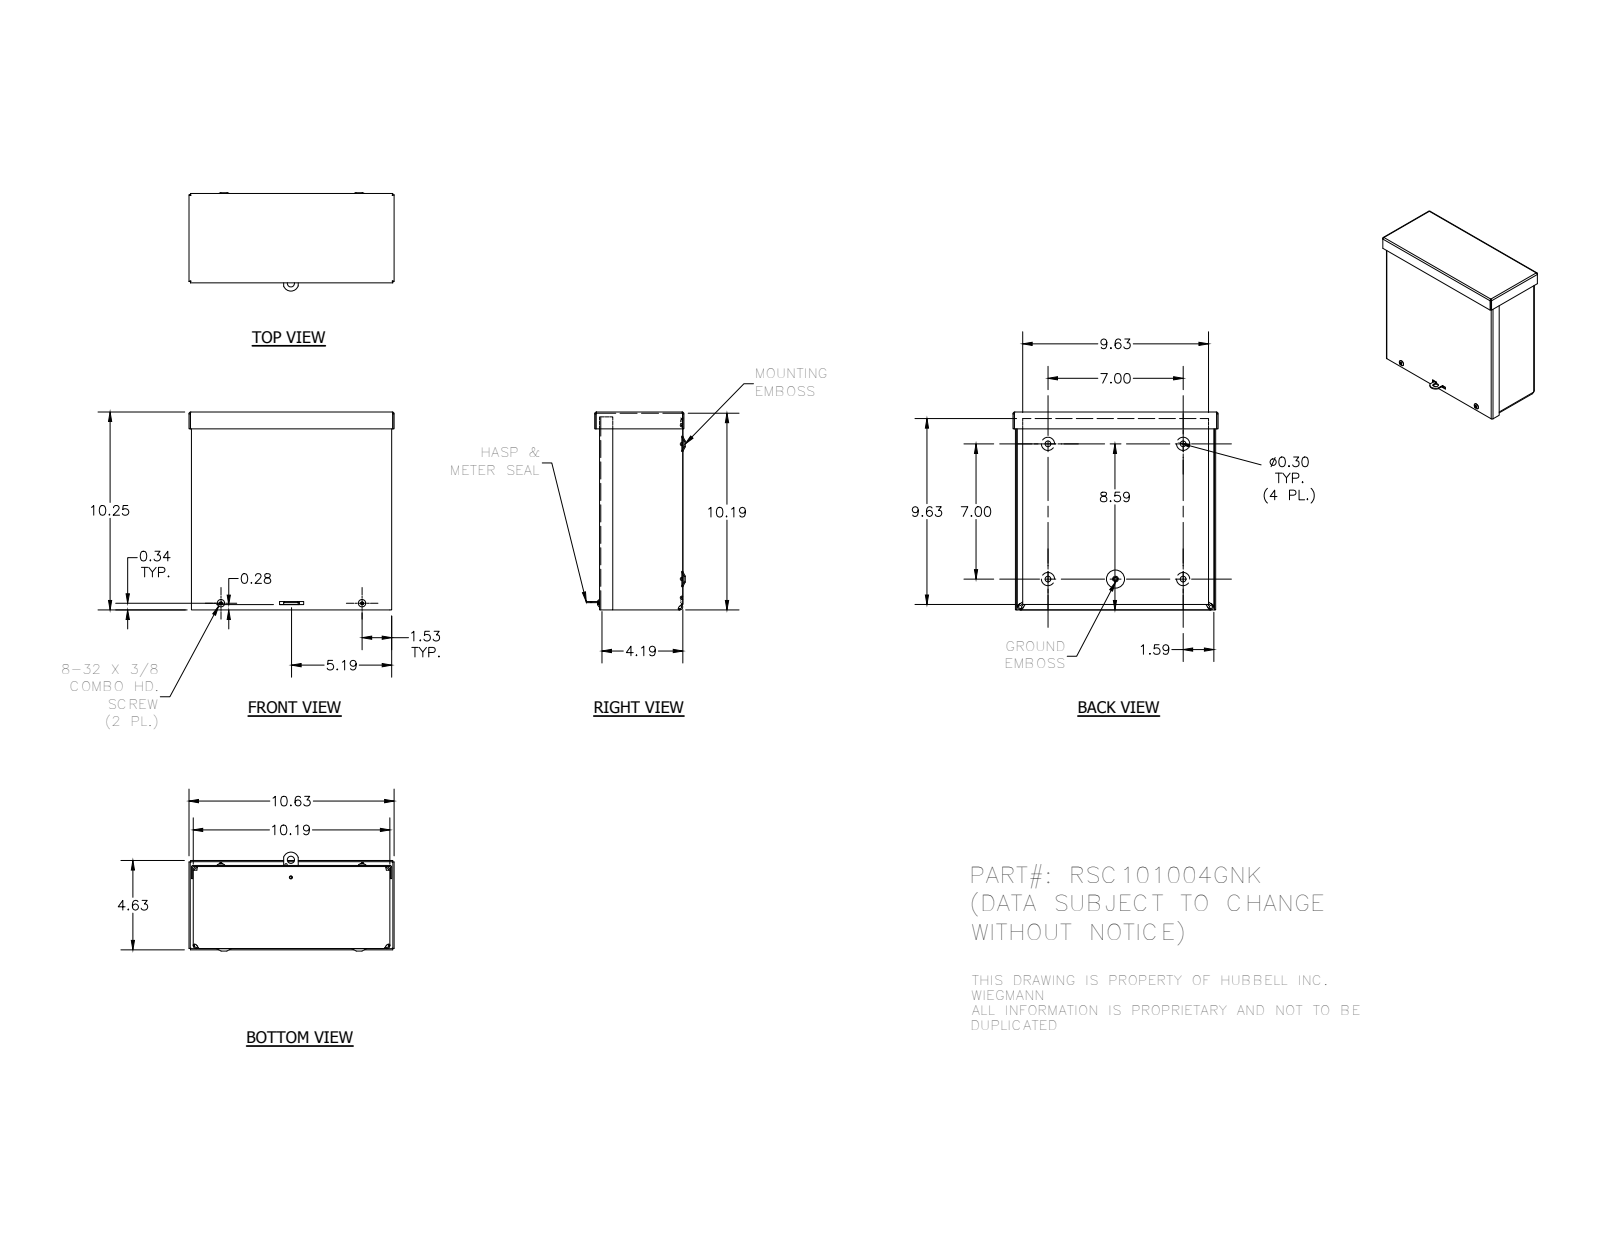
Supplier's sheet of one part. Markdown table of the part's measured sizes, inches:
| quantity | value |
| --- | --- |
| part name | RSC101004GNK_WRAP; RSC1010GNK_LID; RSC1004GNK_CAP; 3183 (+3 more) |
| STEP written by | Autodesk Inventor 2014 (AUTOMOTIVE_DESIGN) |
| units | inches |
| bodies | 7 solids, 377 faces (163 planar, 78 cylindrical, 136 other) |
| overall size | 10.625 × 10.25 × 5.125 |
| volume | 31.39 in³ |
| surface area | 1 027 in² |
| round holes (diameter × count) | 0.3 × 4, 0.313 × 4, 0.125 × 2, 0.148 × 2, 0.156 × 1, 0.165 × 1, 0.375 × 1 |
| round bosses / shafts (diameter × count) | 0.384 × 2, 0.164 × 2, 0.228 × 1 |
| partial cylindrical surfaces (radius × count) | 0.031 × 8, 0.093 × 8, 0.125 × 8, 0.187 × 8, 0.055 × 4, 0.062 × 4, 0.094 × 4, 0.117 × 4 |
| main face-to-face distances | 0.062, 10.126, 0.062, 4.249, 4.187, 0.063, 4.312, 4.25, 10.188, 0.124 |
| hole center spacings | 7, 1.072, 1.261, 3.5, 7.313, 7.826, 8.063, 8.253 |
